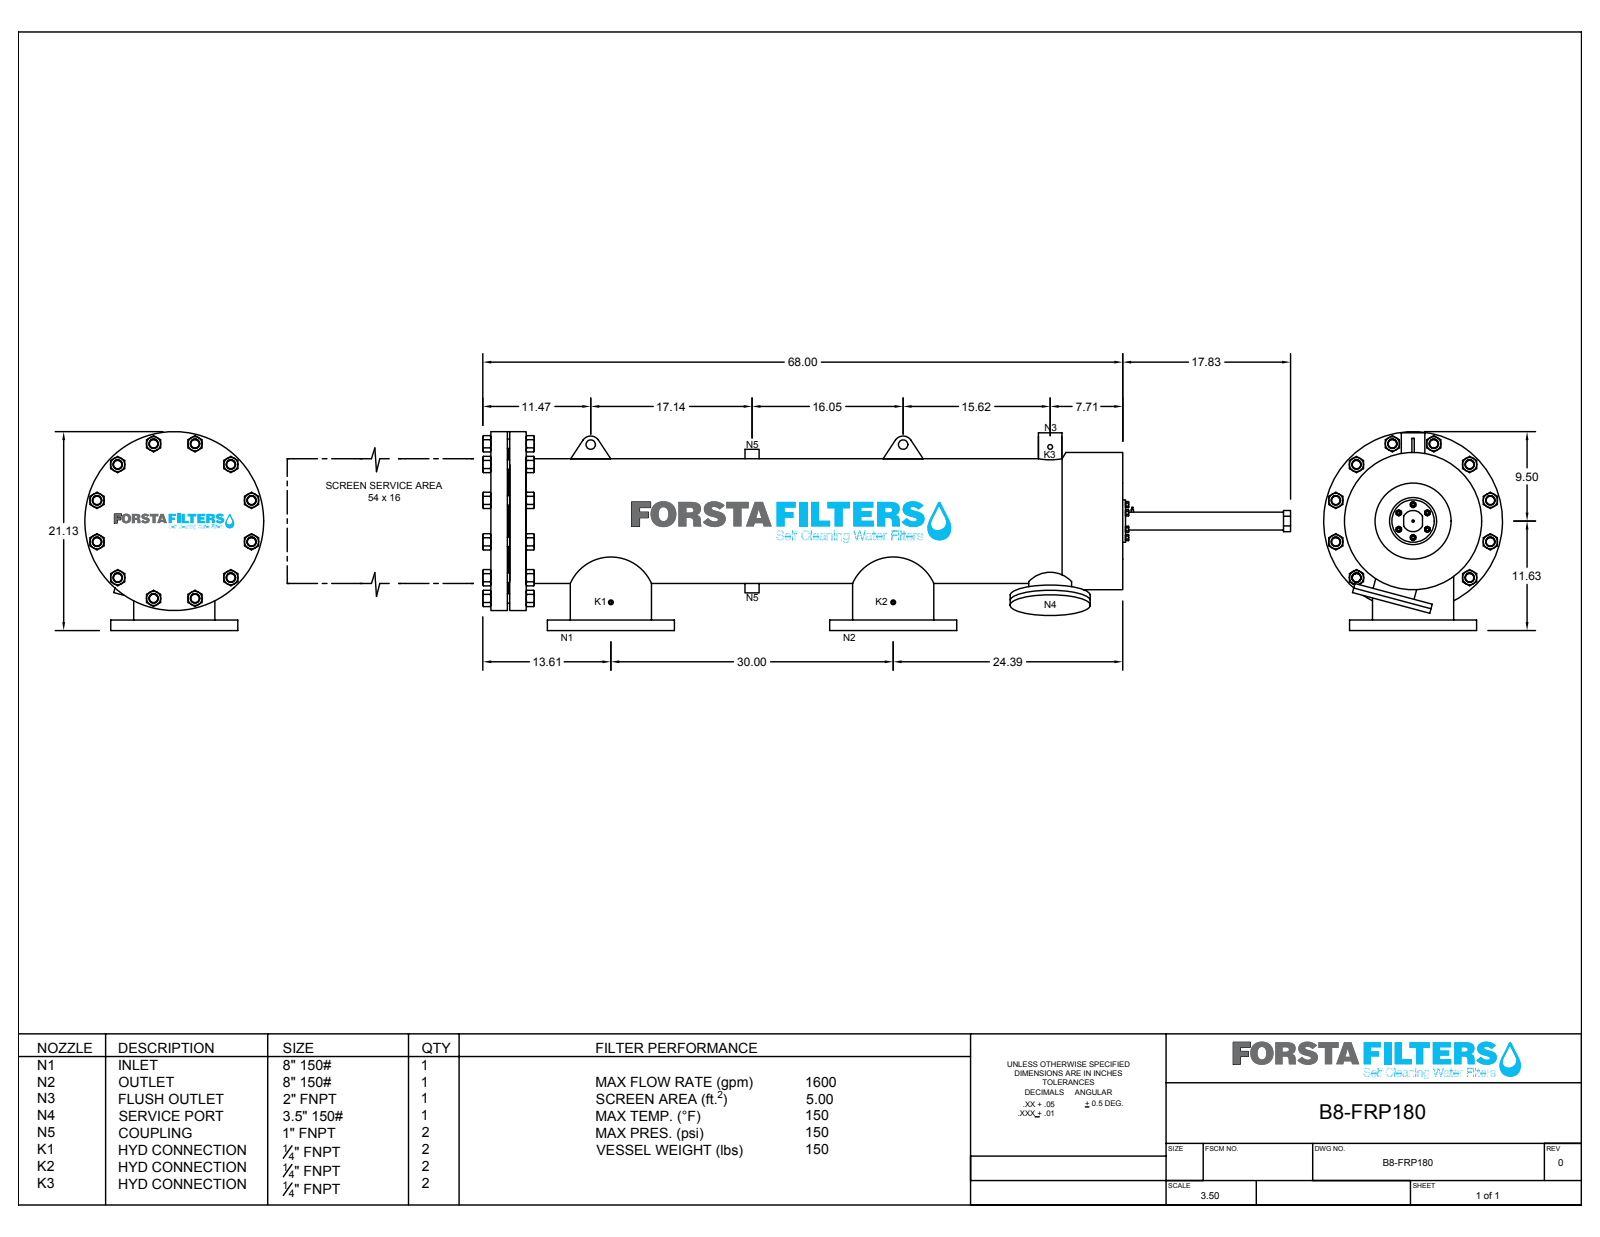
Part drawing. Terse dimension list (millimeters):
name: B8-FRP-180
written by: SolidWorks 2018 (CONFIG_CONTROL_DESIGN)
unit: mm
bodies: 43 solids, 659 faces (311 planar, 338 cylindrical, 10 other)
size: 2088.3 × 536.7 × 482.6
volume: 28 050 000 mm³; area: 5 723 000 mm²
holes: 16× ⌀19.1, 16× ⌀22.4, 15× ⌀25.4, 6× ⌀9.5, 5× ⌀9.5, 2× ⌀6.2, 2× ⌀6.4, 2× ⌀101.6, 2× ⌀203.2, 1× ⌀38.4, 1× ⌀50.8, 1× ⌀326.5
bosses: 2× ⌀330.2, 2× ⌀228.6, 2× ⌀213.2, 2× ⌀111.6, 2× ⌀16.3, 1× ⌀482.6, 1× ⌀370.4, 1× ⌀114.4
rounds: 2× R25.4, 1× R28.6
face distances: 50.8, 44.5, 6.4, 12.7, 1618.3, 1573.8, 1567.5, 95.3, 1523, 5
hole spacings: 72.9, 95.3, 134.7, 176, 215.9, 44.5, 114.2, 149.2
